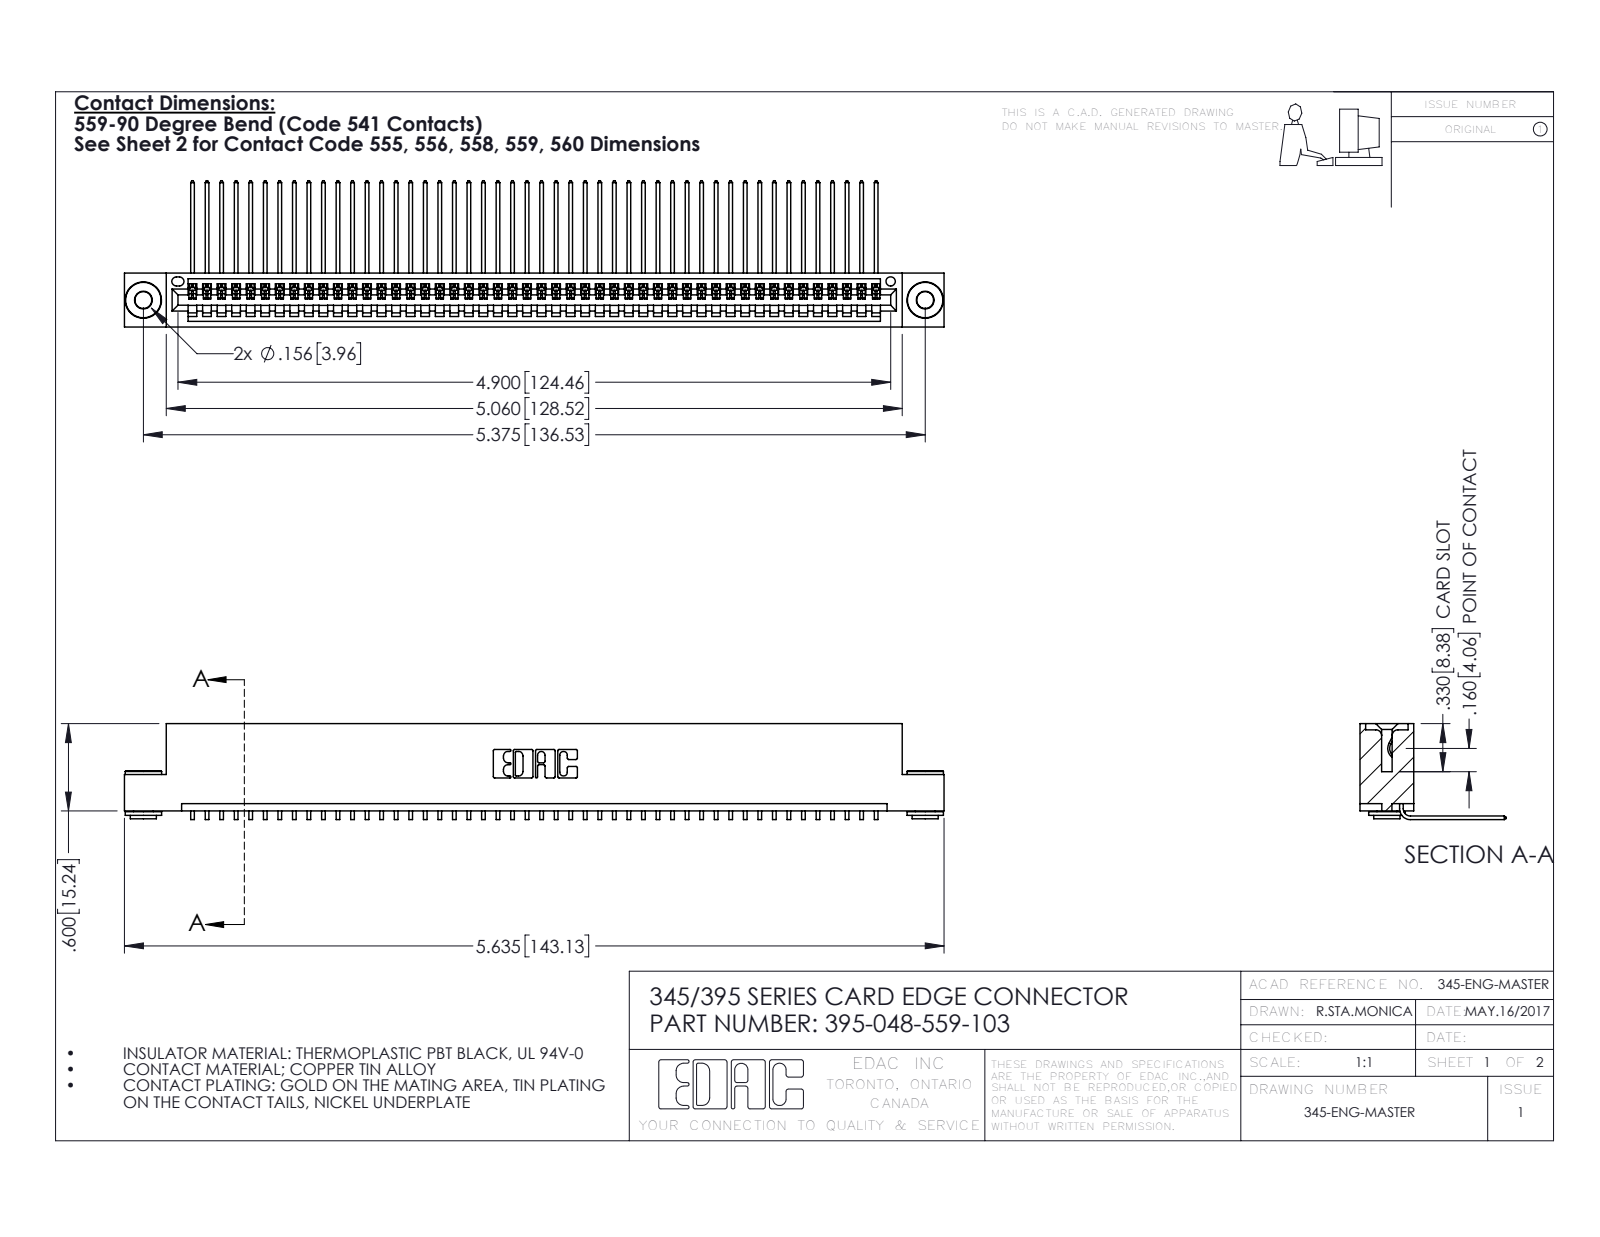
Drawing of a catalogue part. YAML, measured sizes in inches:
part_name: "345-292-001_558 559 Tail - 1; 395-048-559-103; 345-250-002_345-250-002-102; 345 Part_Flush Mounting Lugs - 0.156 Dia-TH"
step_written_by: "SolidWorks 2016 (CONFIG_CONTROL_DESIGN)"
units: inches
bodies: {solids: 51, faces: 3044, planar: 2106, cylindrical: 930, other: 8}
overall_size: [5.635, 1.005, 0.659]
volume: 0.844
surface_area: 30.39
round_holes:
  - {diameter: 0.116, count: 2}
  - {diameter: 0.156, count: 2}
  - {diameter: 0.064, count: 1}
round_bosses_or_shafts:
  - {diameter: 0.25, count: 2}
  - {diameter: 0.18, count: 2}
  - {diameter: 0.136, count: 2}
partial_cylinders:
  - {radius: 0.006, count: 96}
  - {radius: 0.01, count: 22}
  - {radius: 0.007, count: 6}
  - {radius: 0.031, count: 6}
  - {radius: 0.026, count: 3}
  - {radius: 0.031, count: 2}
  - {radius: 0.04, count: 2}
  - {radius: 0.014, count: 1}
face_to_face_distances: [0.072, 0.298, 0.37, 0.2, 0.025, 0.098, 0.272, 0.225, 0.149, 0.072]
hole_center_spacings: [0.27, 5.139, 5.375]
